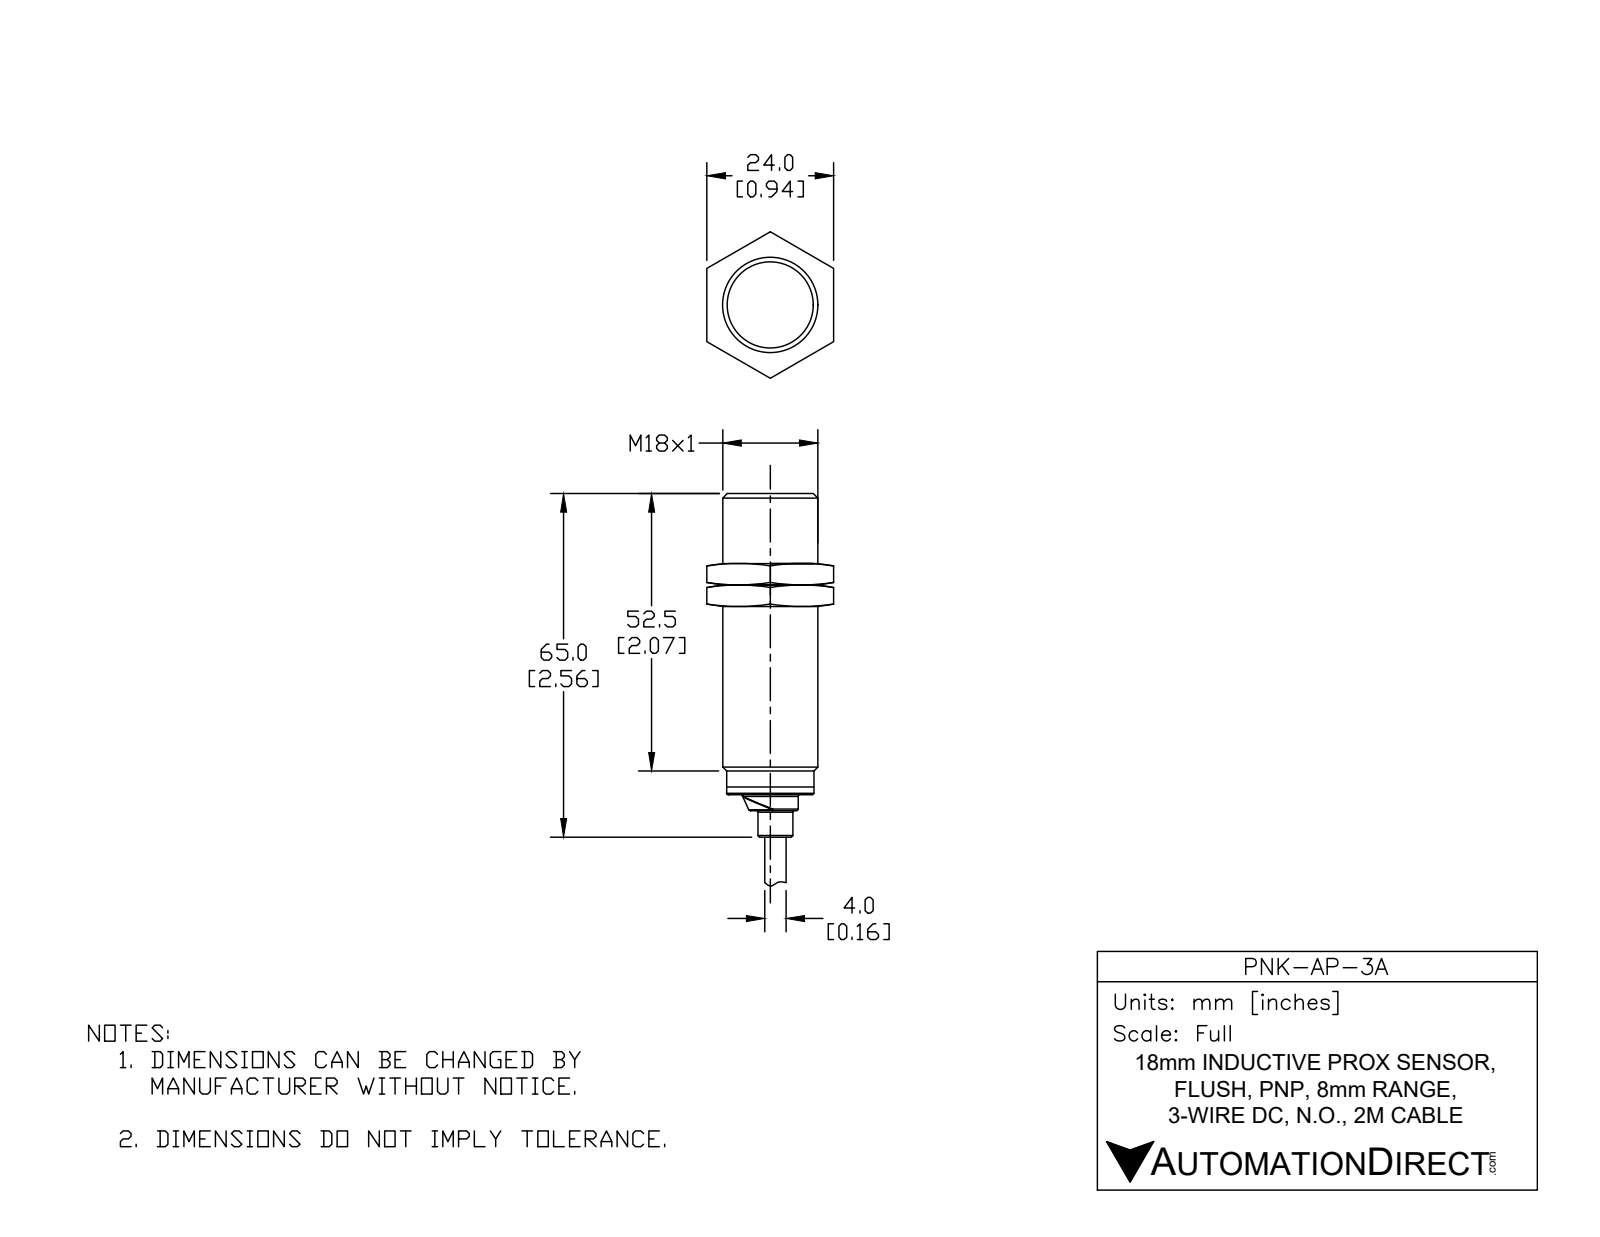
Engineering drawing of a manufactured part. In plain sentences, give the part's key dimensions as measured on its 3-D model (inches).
The part is named "PNK-AP-3A". Its 3-D file was written by "SolidWorks 2017 (AUTOMOTIVE_DESIGN)". It is 1 solid with 76 faces: 18 planar, 20 cylindrical and 38 other. Overall it measures 4.559 by 0.709 by 0.709 inches. Its volume is 0.936 cubic inches and its surface area 7.094 square inches. Round holes: 1 of diameter 0.634. Round bosses or shafts: 1 of diameter 0.709, 1 of diameter 0.65, 1 of diameter 0.65, 1 of diameter 0.633, 1 of diameter 0.417, 1 of diameter 0.26, 1 of diameter 0.157. Partial cylindrical surfaces (rounded edges, fillets, slot ends): 1 of radius 0.079, 1 of radius 0.081, 1 of radius 0.091. The main face-to-face distances are 2.244, 2.362, 0.118, 2.559, 0.315, 0.197, 4.559, 2.315, 2.197, 2.
